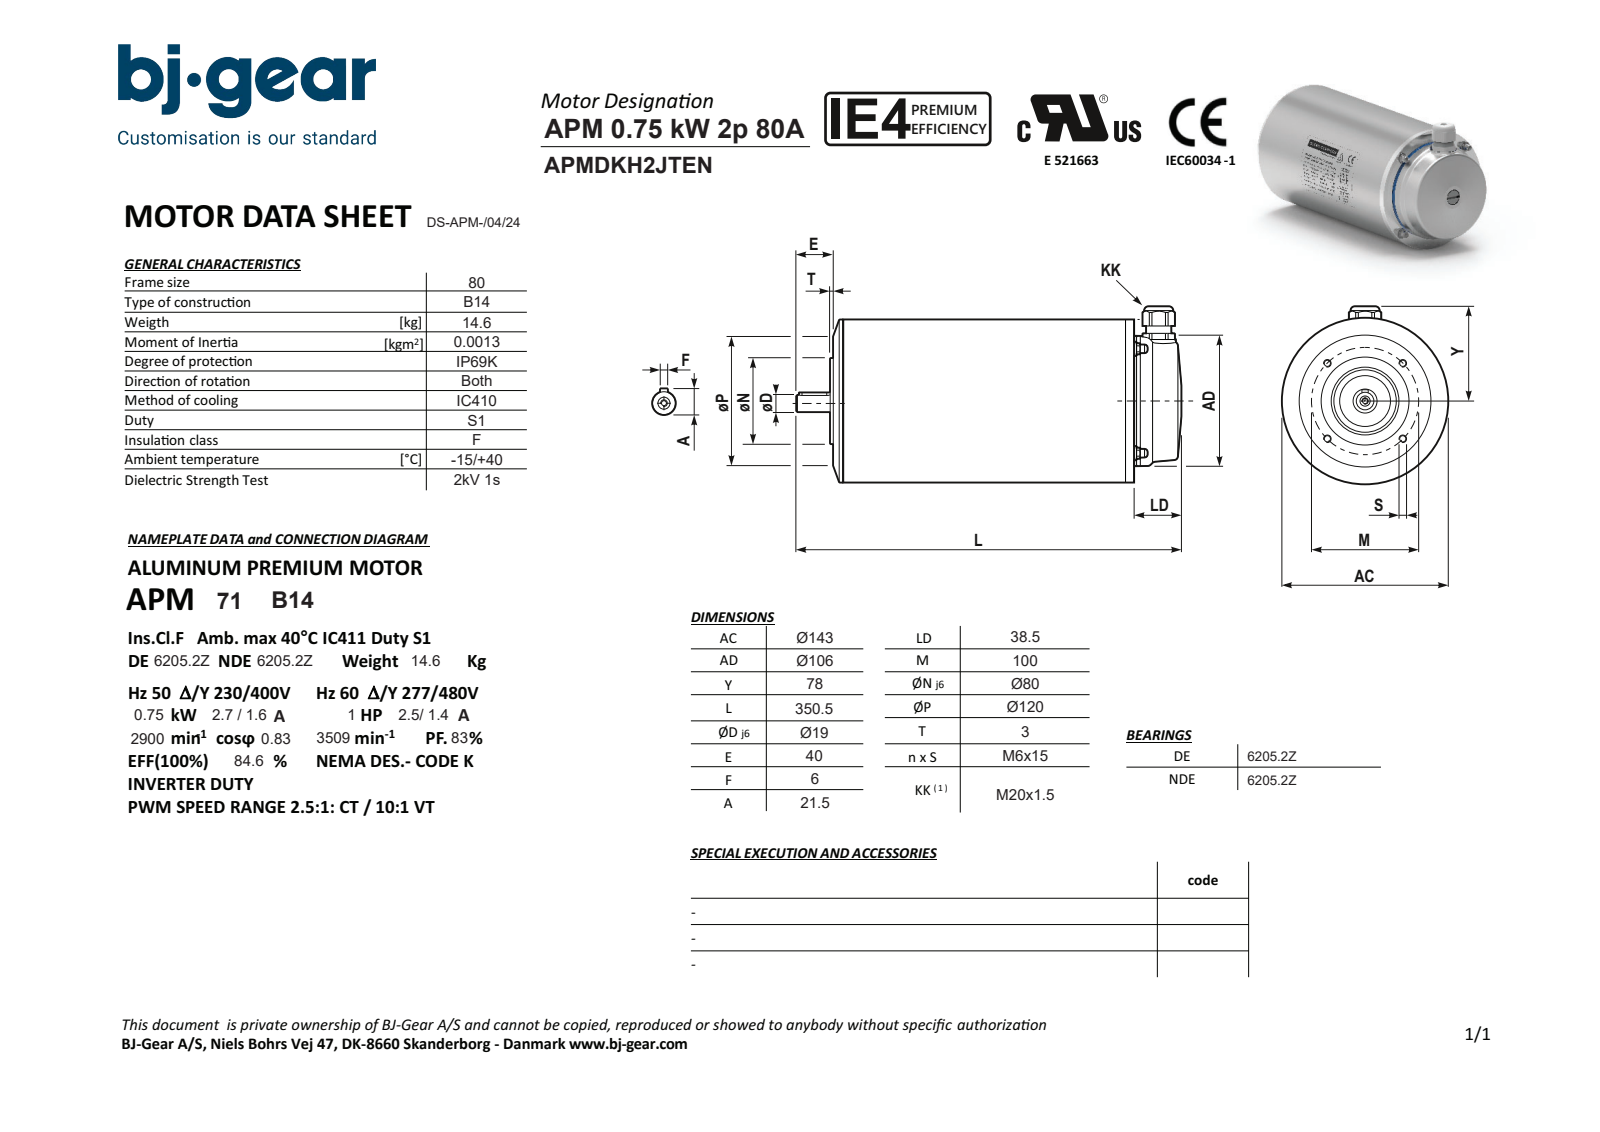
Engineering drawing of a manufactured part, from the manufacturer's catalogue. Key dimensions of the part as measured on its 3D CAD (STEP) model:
Part name (STEP PRODUCT): APMDKH2JTENN4KCR2-N---NNN
STEP written by: Solid Edge (AUTOMOTIVE_DESIGN)
Units: millimetres
Bodies: 1 solid, 156 faces (75 planar, 50 cylindrical, 31 other)
Overall size (bounding box): 350.5 × 148.3 × 142.6
Volume: 4 636 000 mm³ · Surface area: 172 344 mm²
Round holes (diameter × count): ⌀4.92 ×5, ⌀6.4 ×1, ⌀16 ×1, ⌀28 ×1, ⌀65 ×1
Round bosses / shafts (diameter × count): ⌀11.5 ×4, ⌀7 ×4, ⌀142.6 ×1, ⌀142.6 ×1, ⌀106 ×1, ⌀80 ×1, ⌀25 ×1, ⌀23.7 ×1
Partial cylindrical surfaces — rounded edges, fillets, slot ends (radius × count): R3 ×2, R13.2 ×1
Main face-to-face distances: 272, 6, 266, 9, 3, 275, 24, 310.5, 38.5, 304.5
Hole centre spacings: 50.01, 70.72, 100.01
